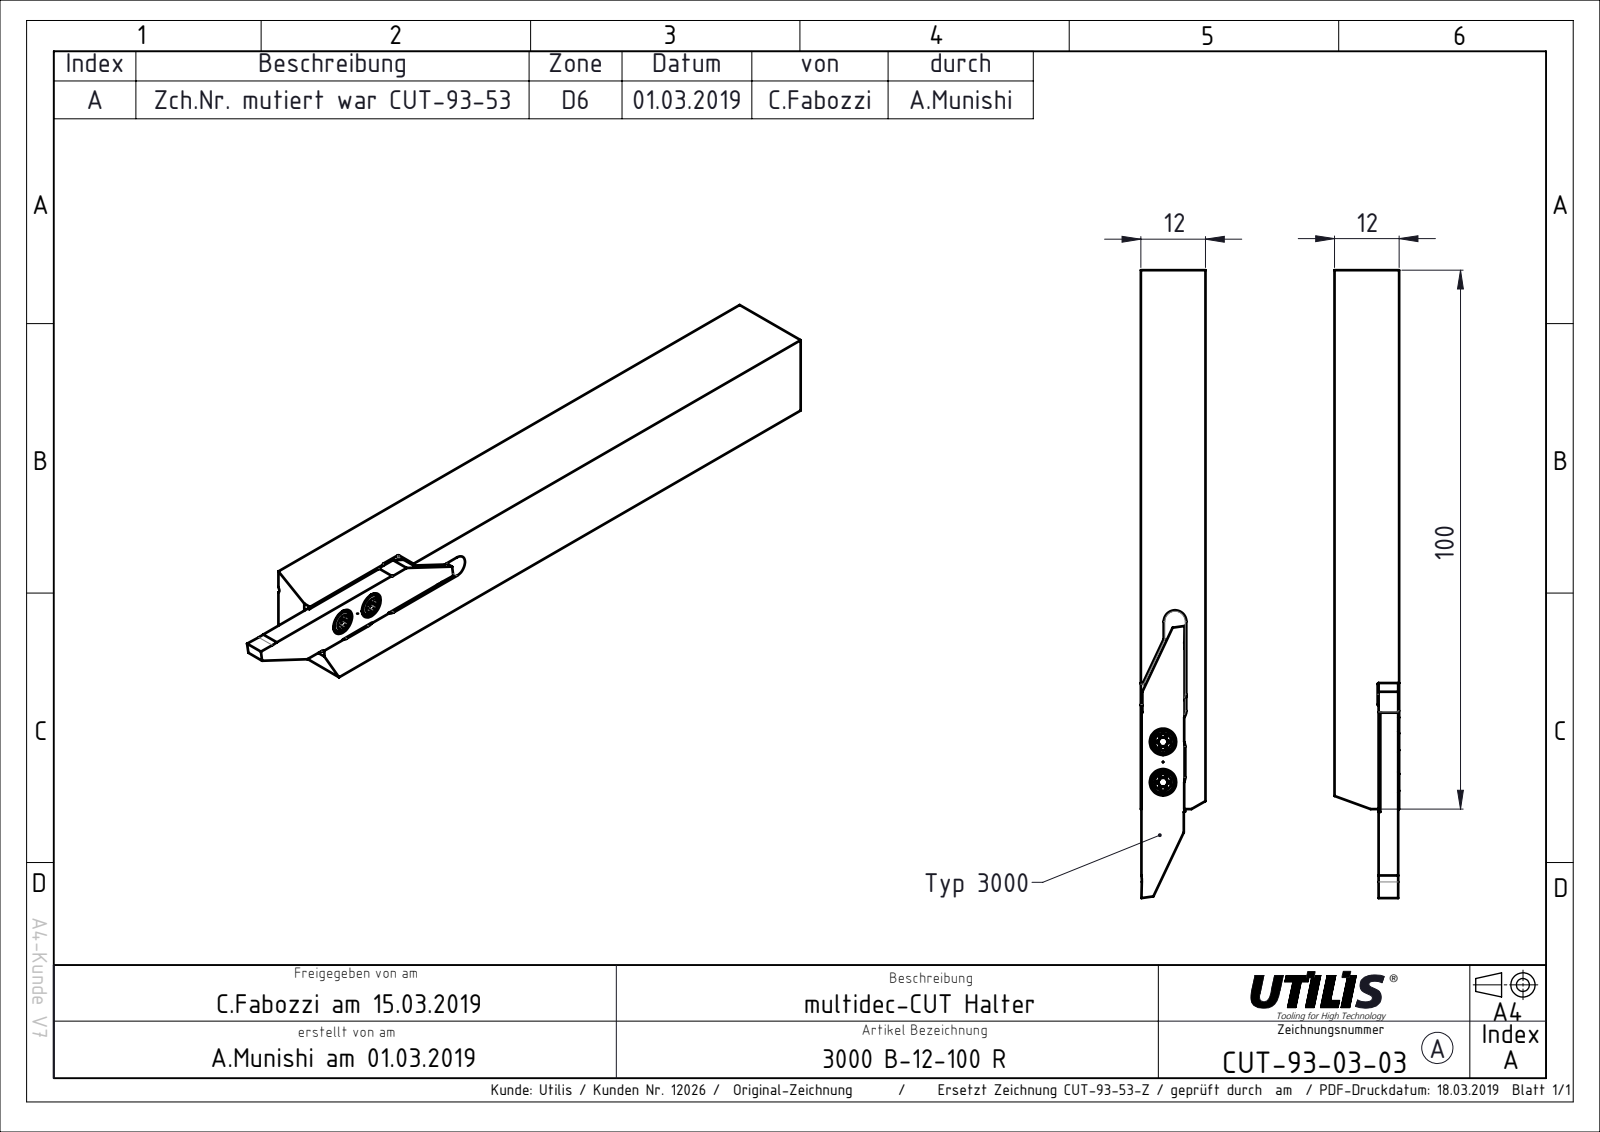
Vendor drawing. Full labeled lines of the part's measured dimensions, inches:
Part name (STEP PRODUCT): CUT-Vorlage 3000 R+L Lang Kunde; CUT-93-Kunde; CUT-93-53; CUT-Vorlage 3000 R+L Lang Kunde_R-Lang (+1 more)
STEP written by: SolidWorks 2015 (CONFIG_CONTROL_DESIGN)
Units: inches
Bodies: 2 solids, 55 faces (36 planar, 19 cylindrical, 0 other)
Overall size (bounding box): 4.587 × 0.472 × 0.472
Volume: 0.87 in³ · Surface area: 9.771 in²
Round holes (diameter × count): ⌀0.098 ×2, ⌀0.193 ×2
Partial cylindrical surfaces — rounded edges, fillets, slot ends (radius × count): R0.083 ×4, R0.006 ×2, R0.394 ×2
Main face-to-face distances: 0.472, 0.15, 0.323, 0.142, 0.465, 0.157, 0.315, 0.14, 0.018, 0.333
Hole centre spacings: 0.148, 0.295
